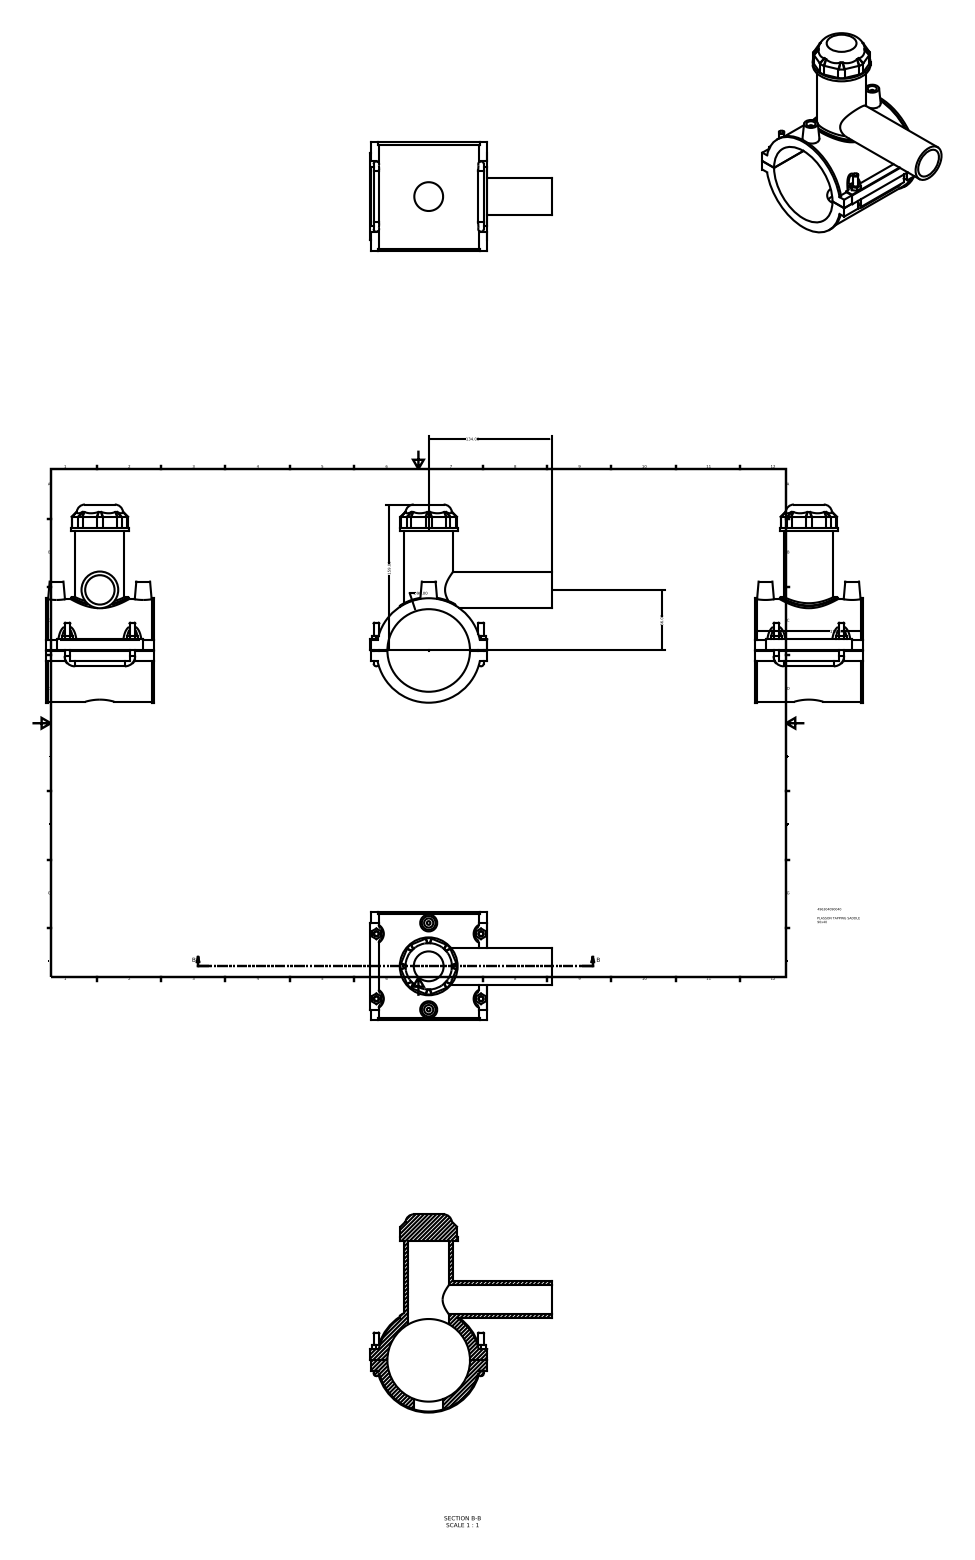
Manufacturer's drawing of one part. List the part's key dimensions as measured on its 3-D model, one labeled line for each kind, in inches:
Part name (STEP PRODUCT): 496304090040
STEP written by: Autodesk Inventor 2015 (AUTOMOTIVE_DESIGN)
Units: inches
Bodies: 1 solid, 224 faces (125 planar, 55 cylindrical, 44 other)
Overall size (bounding box): 8.501 × 7.795 × 4.646
Volume: 37.09 in³ · Surface area: 245.5 in²
Round holes (diameter × count): ⌀0.394 ×2, ⌀1.235 ×1, ⌀1.26 ×1, ⌀1.736 ×1, ⌀3.543 ×1
Round bosses / shafts (diameter × count): ⌀0.236 ×6, ⌀0.157 ×2, ⌀4.481 ×1, ⌀4.394 ×1, ⌀2.48 ×1, ⌀2.108 ×1, ⌀1.575 ×1
Partial cylindrical surfaces — rounded edges, fillets, slot ends (radius × count): R0.354 ×8, R0.118 ×4, R0.295 ×4, R0.02 ×1, R2.285 ×1
Main face-to-face distances: 4.646, 0.039, 5.14, 5.136, 5, 0.441, 0.445, 5.581, 0.925, 0.484
Hole centre spacings: 1.858, 3.717
